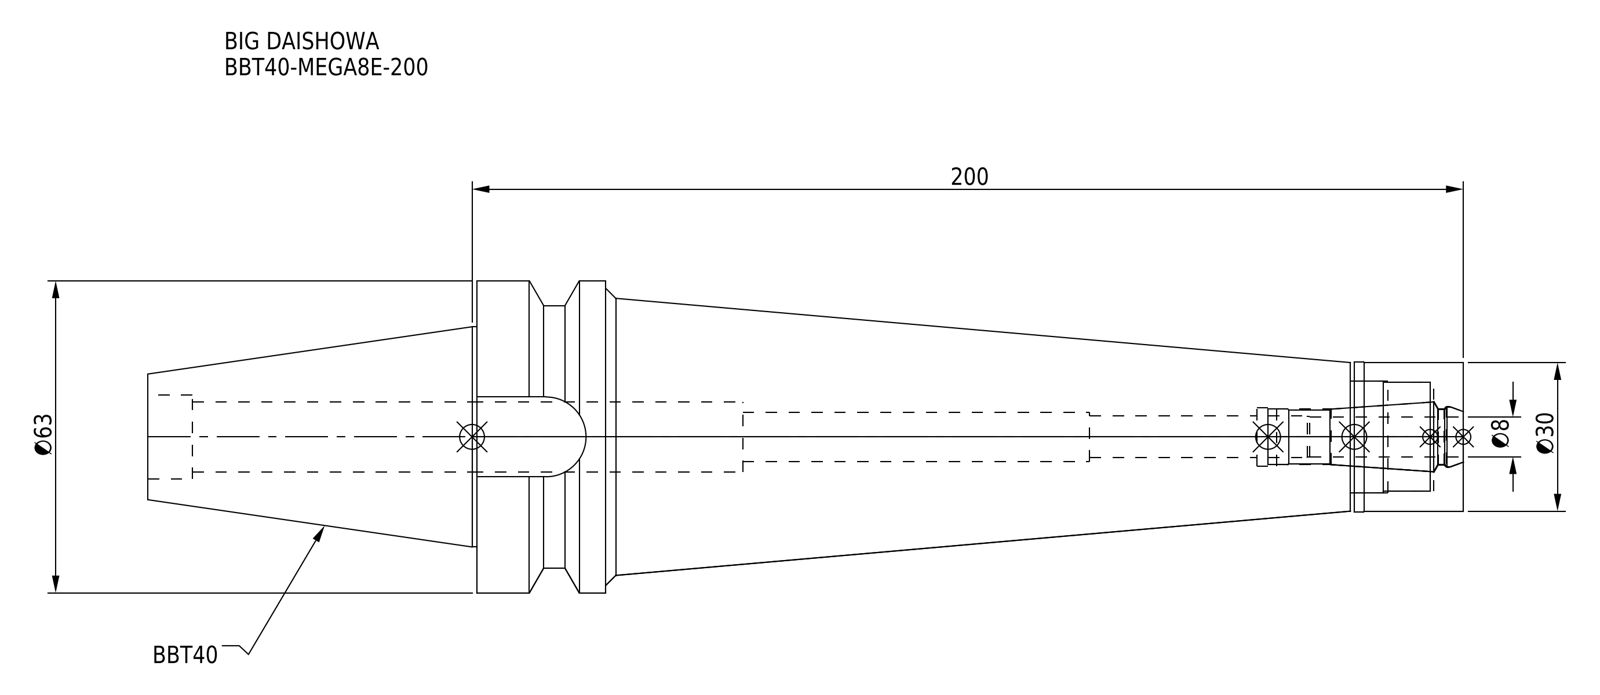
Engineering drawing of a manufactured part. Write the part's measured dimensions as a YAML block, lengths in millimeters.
part_name: "MEN8_1.stp; DXF_TEMP_ASSY_ASM_4_ASM.stp; BBT40-MEGA8E-200; BBT40ME08200-080_ASM.stp (+3 more)"
step_written_by: "SolidWorks 2019 (CONFIG_CONTROL_DESIGN)"
units: millimeters
bodies: {solids: 2, faces: 81, planar: 21, cylindrical: 40, other: 20}
overall_size: [265.4, 63, 63]
volume: 346205
surface_area: 52770
round_holes:
  - {diameter: 8.4, count: 1}
  - {diameter: 10, count: 1}
  - {diameter: 11.2, count: 1}
  - {diameter: 11.4, count: 1}
  - {diameter: 11.8, count: 1}
  - {diameter: 12.3, count: 1}
  - {diameter: 14.2, count: 1}
  - {diameter: 17, count: 1}
  - {diameter: 22, count: 1}
  - {diameter: 22.5, count: 1}
round_bosses_or_shafts:
  - {diameter: 63, count: 1}
  - {diameter: 53, count: 1}
  - {diameter: 44.45, count: 1}
  - {diameter: 30.3, count: 1}
  - {diameter: 30, count: 1}
partial_cylinders:
  - {radius: 8.05, count: 1}
face_to_face_distances: [199, 16.1, 45, 22, 177, 22.8, 0.8, 176.2, 173, 151]
